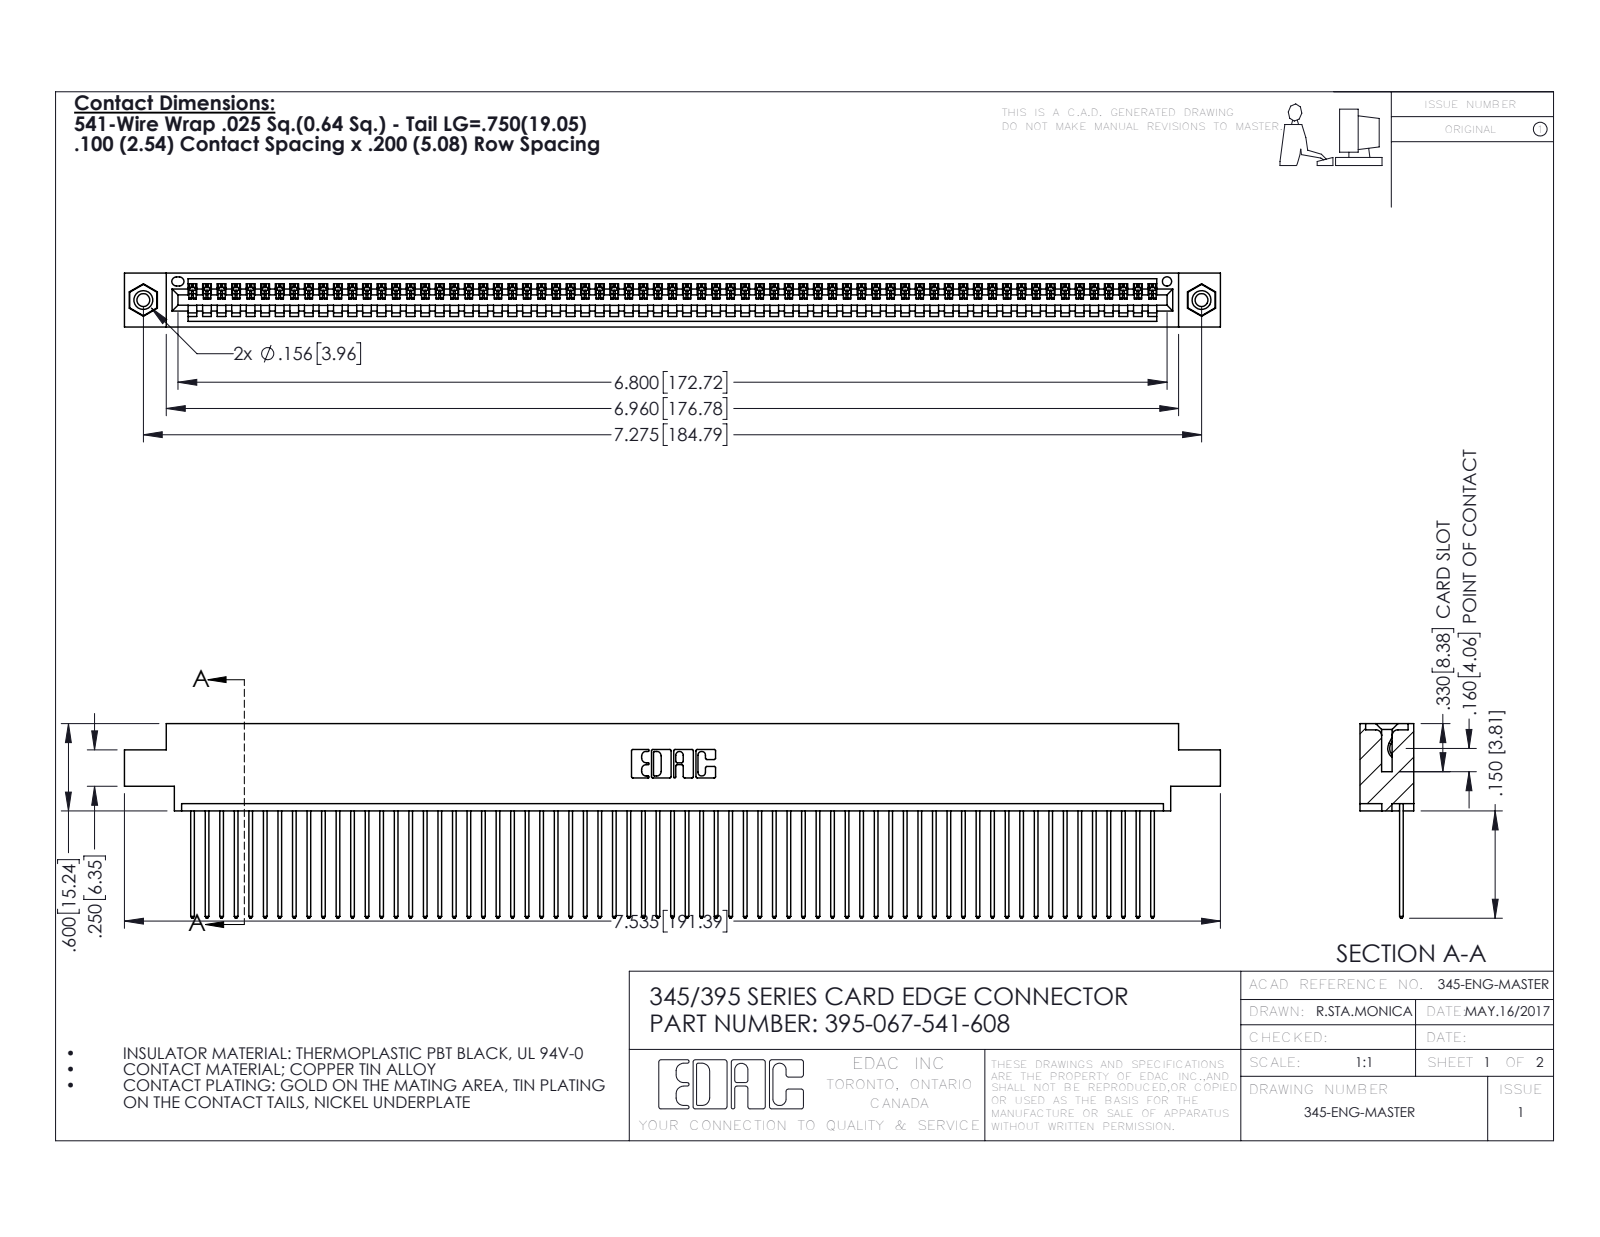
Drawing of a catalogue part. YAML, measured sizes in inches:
part_name: "345-292-001_345-293-141; 395-067-541-608; 345 Part_0.170 Offset - 0.156 Dia-TI; 345-250-001_345-250-003-102"
step_written_by: "SolidWorks 2016 (CONFIG_CONTROL_DESIGN)"
units: inches
bodies: {solids: 70, faces: 4076, planar: 2796, cylindrical: 1264, other: 16}
overall_size: [7.535, 1.337, 0.37]
volume: 1.128
surface_area: 40.84
round_holes:
  - {diameter: 0.089, count: 2}
  - {diameter: 0.125, count: 2}
  - {diameter: 0.156, count: 2}
  - {diameter: 0.064, count: 1}
round_bosses_or_shafts:
  - {diameter: 0.155, count: 2}
partial_cylinders:
  - {radius: 0.006, count: 134}
  - {radius: 0.01, count: 134}
  - {radius: 0.01, count: 22}
  - {radius: 0.007, count: 6}
  - {radius: 0.031, count: 6}
  - {radius: 0.026, count: 3}
  - {radius: 0.031, count: 2}
  - {radius: 0.04, count: 2}
face_to_face_distances: [0.072, 0.298, 0.098, 0.272, 0.025, 0.37, 0.2, 0.225, 0.175, 0.149]
hole_center_spacings: [0.27, 7.039, 7.275]
